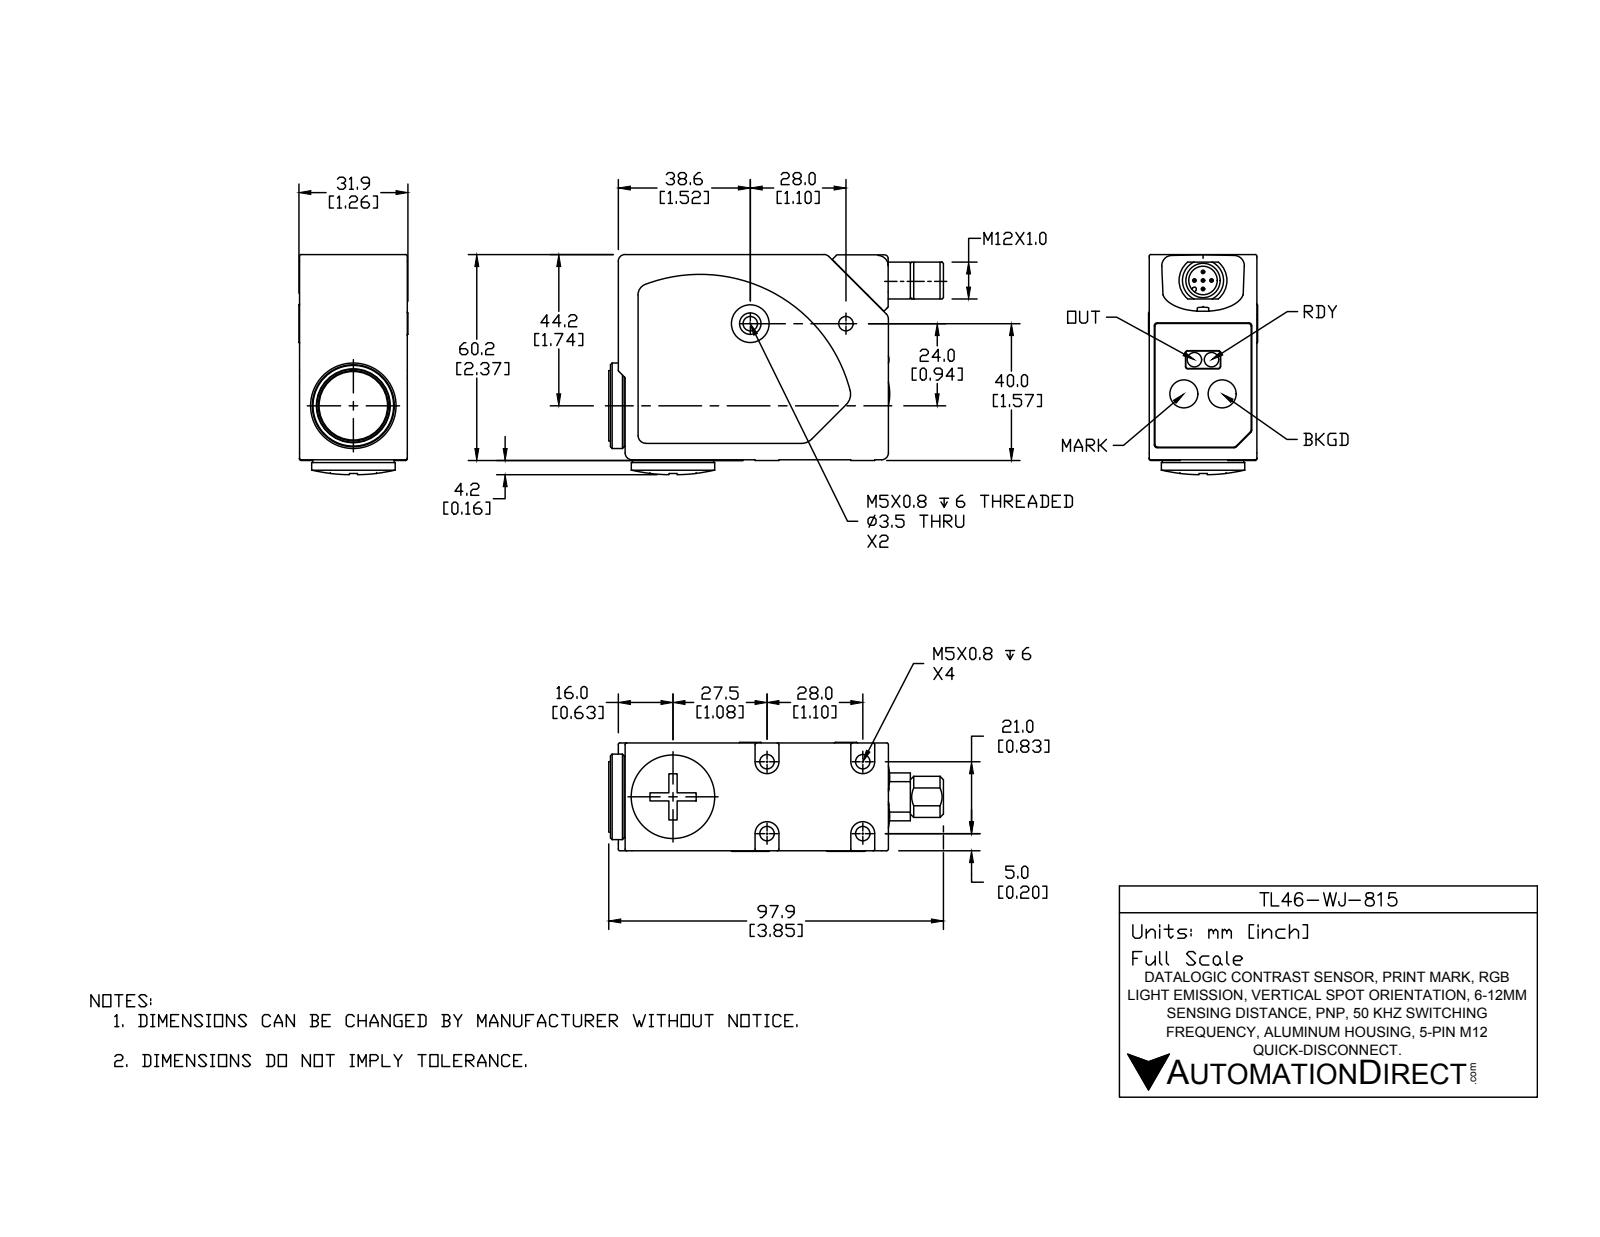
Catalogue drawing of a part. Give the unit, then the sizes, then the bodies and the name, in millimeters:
Units: millimetres
Overall size (bounding box): 97.9 × 64.37 × 31.9
Round holes (diameter × count): ⌀4.2 ×8, ⌀8.2 ×2, ⌀8.3 ×1, ⌀20 ×1
Round bosses / shafts (diameter × count): ⌀1 ×5, ⌀23.8 ×2, ⌀25 ×1, ⌀24.4 ×1, ⌀19 ×1, ⌀11 ×1
Partial cylindrical surfaces — rounded edges, fillets, slot ends (radius × count): R0.5 ×32, R0.8 ×10, R0.6 ×5, R2 ×5, R0.51 ×4, R3.5 ×4, R6 ×1, R7 ×1
Main face-to-face distances: 31.3, 31.1, 31.5, 60, 79, 77, 2, 0.4, 31.7, 60.2
Hole centre spacings: 28, 6.58, 10.47, 12.87, 13.68, 21, 23.29, 33.63
Volume: 148 607 mm³ · Surface area: 21 597 mm²
Bodies: 7 solids, 332 faces (96 planar, 128 cylindrical, 108 other)
Part name (STEP PRODUCT): TL46-WJ-815
STEP written by: SolidWorks 2016 (AUTOMOTIVE_DESIGN)
